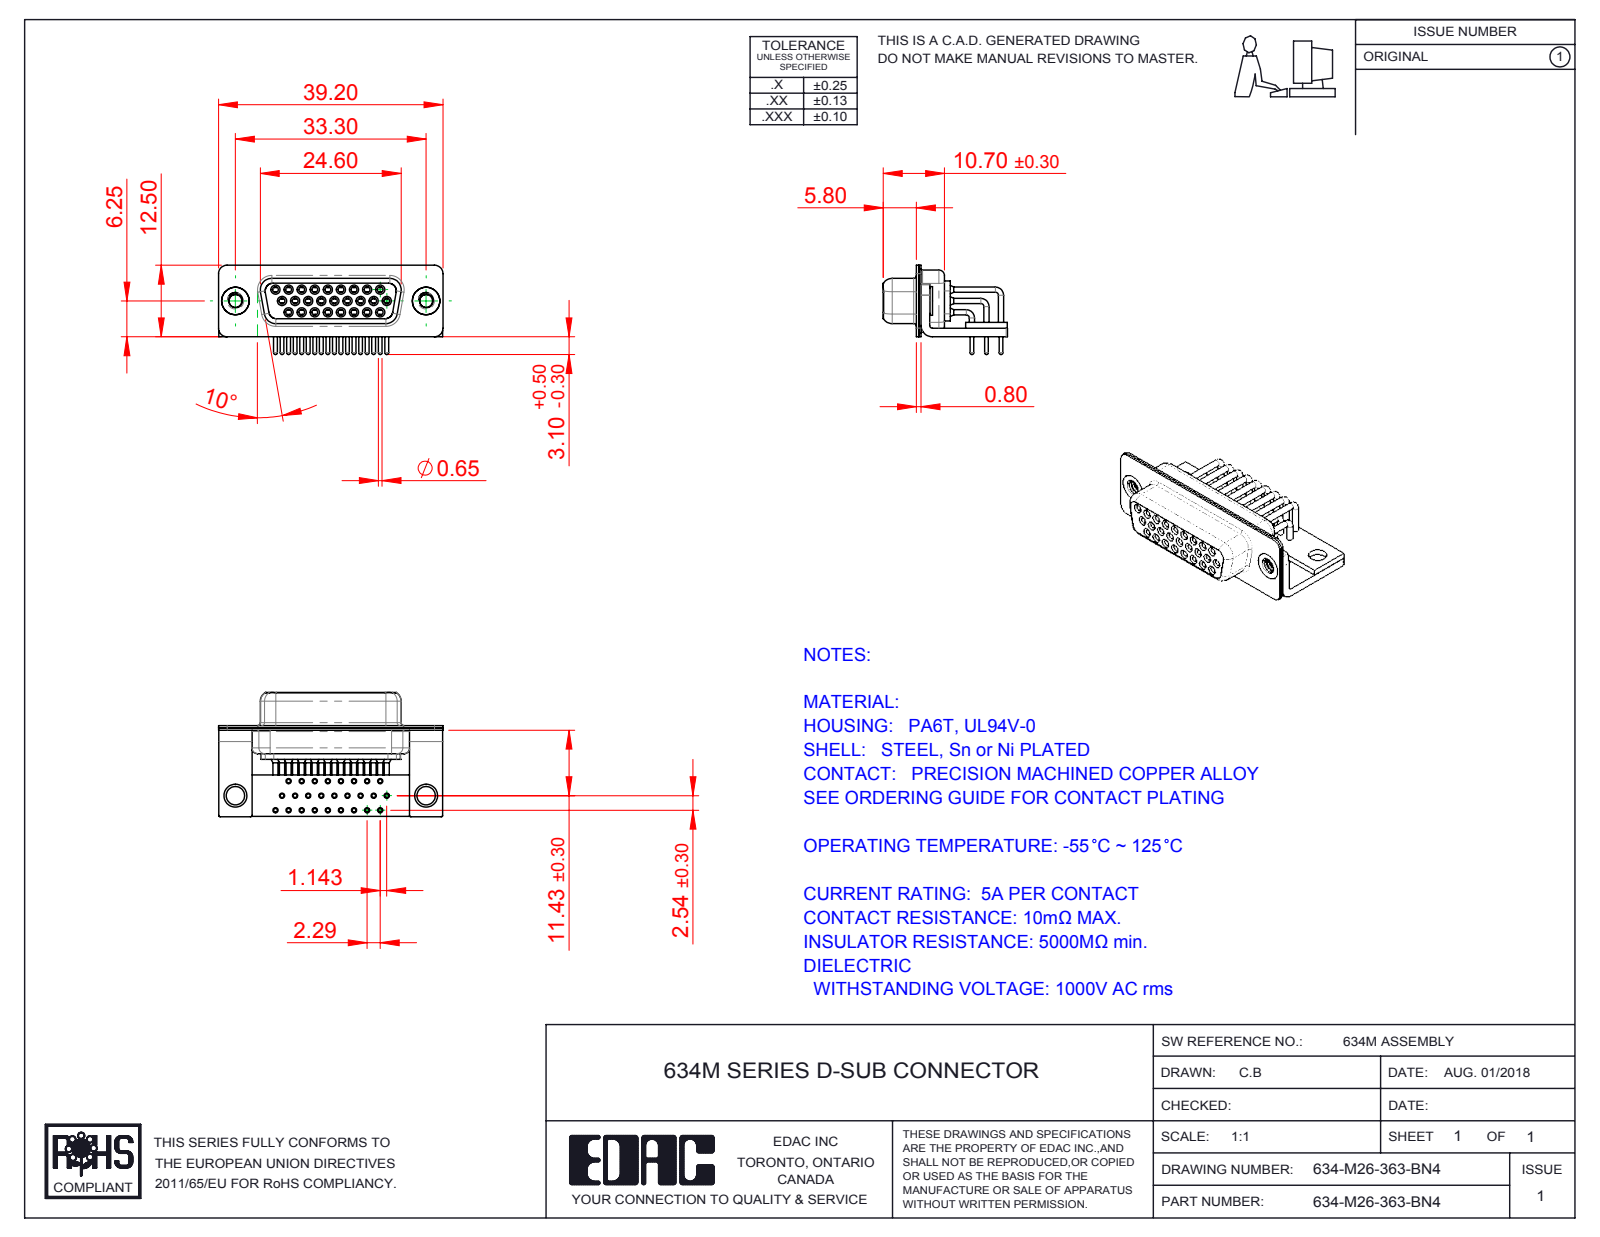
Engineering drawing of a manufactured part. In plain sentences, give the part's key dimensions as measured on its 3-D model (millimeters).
The part is named "634M Shell Rear_26 Contacts; 634M Contact Row 3; 634M Stabilizer Board_26 Contacts; 634M 4-40 Threaded Rivet_Stabilizer (+6 more)". Its 3-D file was written by "SolidWorks 2016 (CONFIG_CONTROL_DESIGN)". It is 34 solids with 1759 faces: 483 planar, 809 cylindrical and 467 other. Overall it measures 39.2 by 21.7 by 15.6 millimeters. Its volume is 3 063 cubic millimeters and its surface area 9 770 square millimeters. Round holes: 26 of diameter 0.9, 26 of diameter 1, 26 of diameter 1.1, 26 of diameter 1.7, 26 of diameter 1.8, 26 of diameter 2, 2 of diameter 2.26, 2 of diameter 3.2, 2 of diameter 4, 2 of diameter 4.8. Round bosses or shafts: 27 of diameter 0.9, 26 of diameter 1.6, 26 of diameter 1.5, 26 of diameter 0.65, 2 of diameter 5, 2 of diameter 4.9, 1 of diameter 2. Partial cylindrical surfaces (rounded edges, fillets, slot ends): 16 of radius 0.25, 16 of radius 1.5, 13 of radius 2, 8 of radius 1.35, 8 of radius 1.6, 5 of radius 0.5, 4 of radius 0.6, 4 of radius 0.65. The main face-to-face distances are 0.4, 2.3, 0.8, 1, 1.5, 1.9, 9.35, 1.45, 8.95, 0.85. The hole center spacings are 4.57, 2.29, 2.28, 3.96, 6.05, 6.86, 4.27, 2.78.
